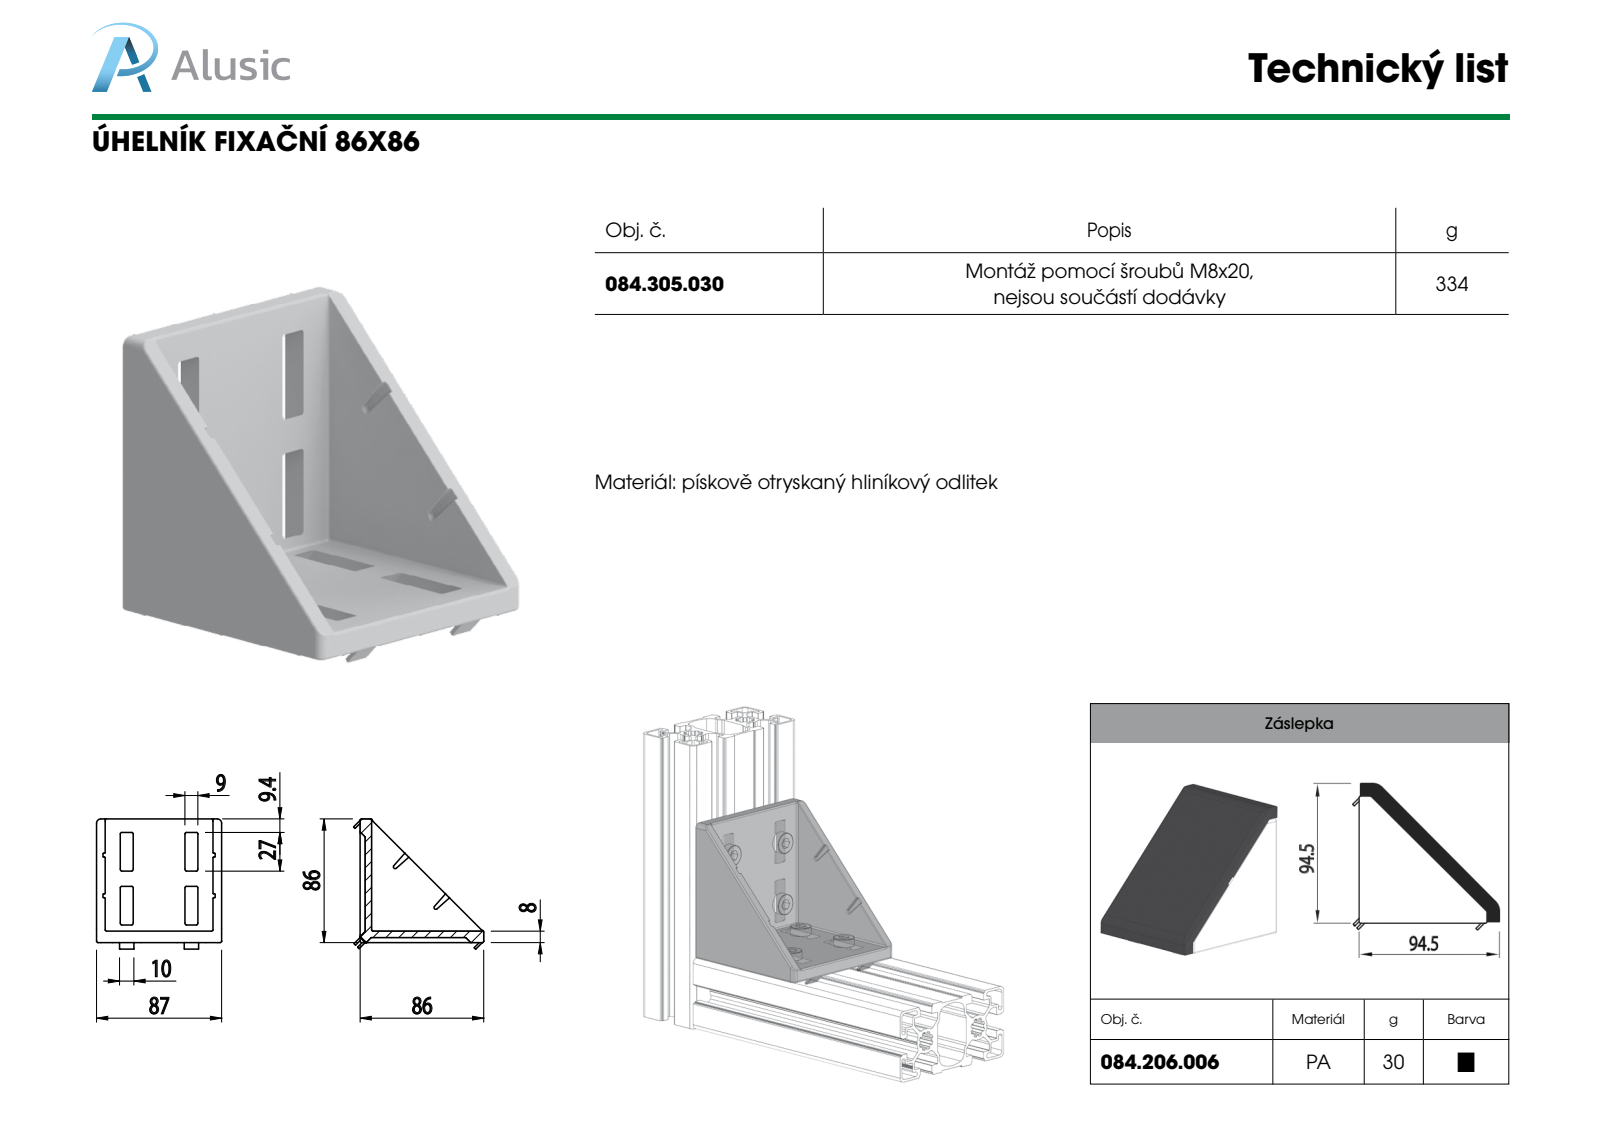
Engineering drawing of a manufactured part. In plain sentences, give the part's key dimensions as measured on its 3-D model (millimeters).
The part is named "084.305.030". Its 3-D file was written by "SolidWorks 2018 (CONFIG_CONTROL_DESIGN)". It is 1 solid with 935 faces: 190 planar, 399 cylindrical and 346 other. Overall it measures 90.51 by 90.51 by 87 millimeters. Its volume is 107 463 cubic millimeters and its surface area 49 404 square millimeters. Round bosses or shafts: 12 of diameter 4. Partial cylindrical surfaces (rounded edges, fillets, slot ends): 151 of radius 0.5, 67 of radius 0.2, 54 of radius 1, 4 of radius 3, 2 of radius 1.25. The main face-to-face distances are 4.5, 6, 81, 87, 3.5, 8, 75, 25.5, 70.5, 45.
